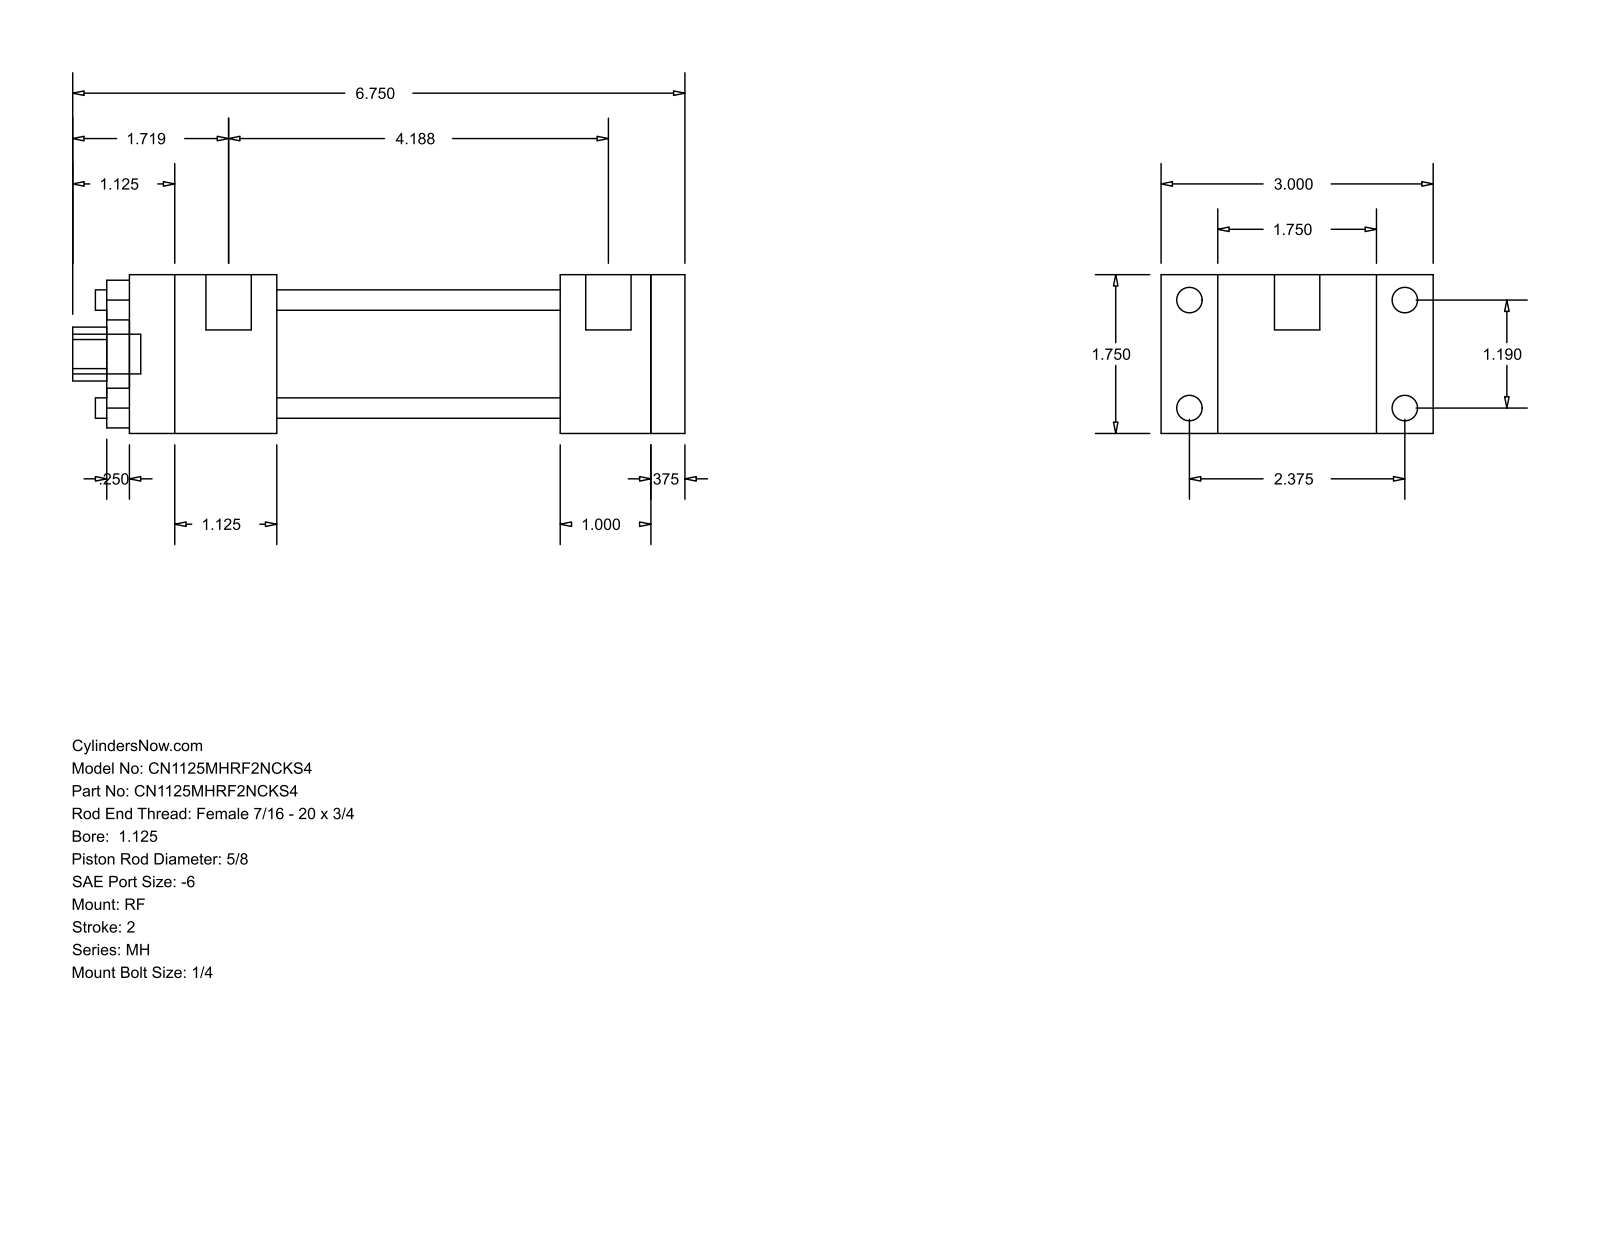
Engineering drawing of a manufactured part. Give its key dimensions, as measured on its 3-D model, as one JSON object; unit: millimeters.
{"part_name": "MH_RF__0112_0.625", "step_written_by": "GSSL Pune (CONFIG_CONTROL_DESIGN)", "units": "millimeters", "bodies": {"solids": 0, "faces": 92, "planar": 64, "cylindrical": 28, "other": 0}, "overall_size": [171.45, 76.2, 44.45], "round_holes": [[5.71, 4], [15.88, 1], [28.57, 1], [34.92, 1]], "round_bosses_or_shafts": [[7.14, 4], [5.56, 4], [12.7, 2], [11.11, 1]], "partial_cylinders_radius": [[7.54, 1]], "face_to_face_distances": [44.46, 9.52, 15.87, 104.78, 114.3, 79.38, 25.4, 34.92, 41.27, 120.65], "hole_center_spacings": [21.37, 30.22, 42.74]}
